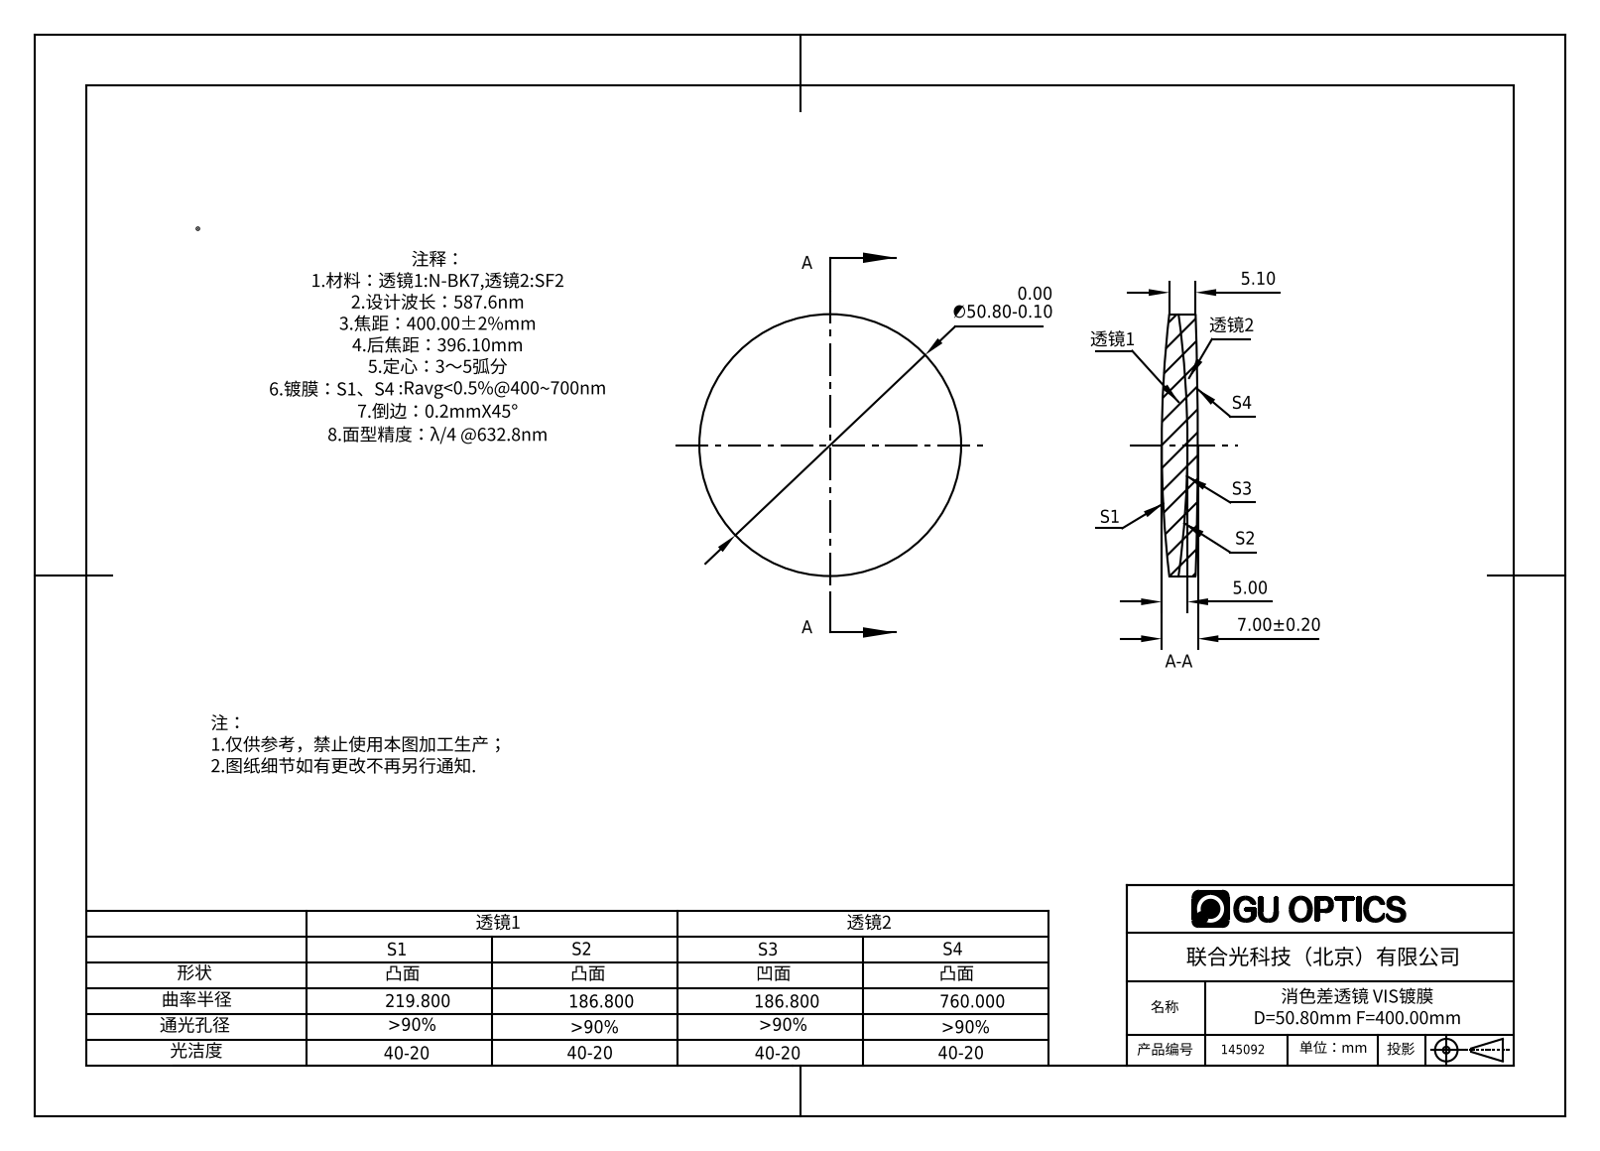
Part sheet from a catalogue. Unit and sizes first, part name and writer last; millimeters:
Units: millimetres
Overall size (bounding box): 50.8 × 50.8 × 7
Round bosses / shafts (diameter × count): ⌀50.8 ×1
Volume: 12 267 mm³ · Surface area: 8 948 mm²
Bodies: 2 solids, 12 faces (0 planar, 4 cylindrical, 8 other)
Part name (STEP PRODUCT): 145092
STEP written by: SolidWorks 2016 (AUTOMOTIVE_DESIGN)
